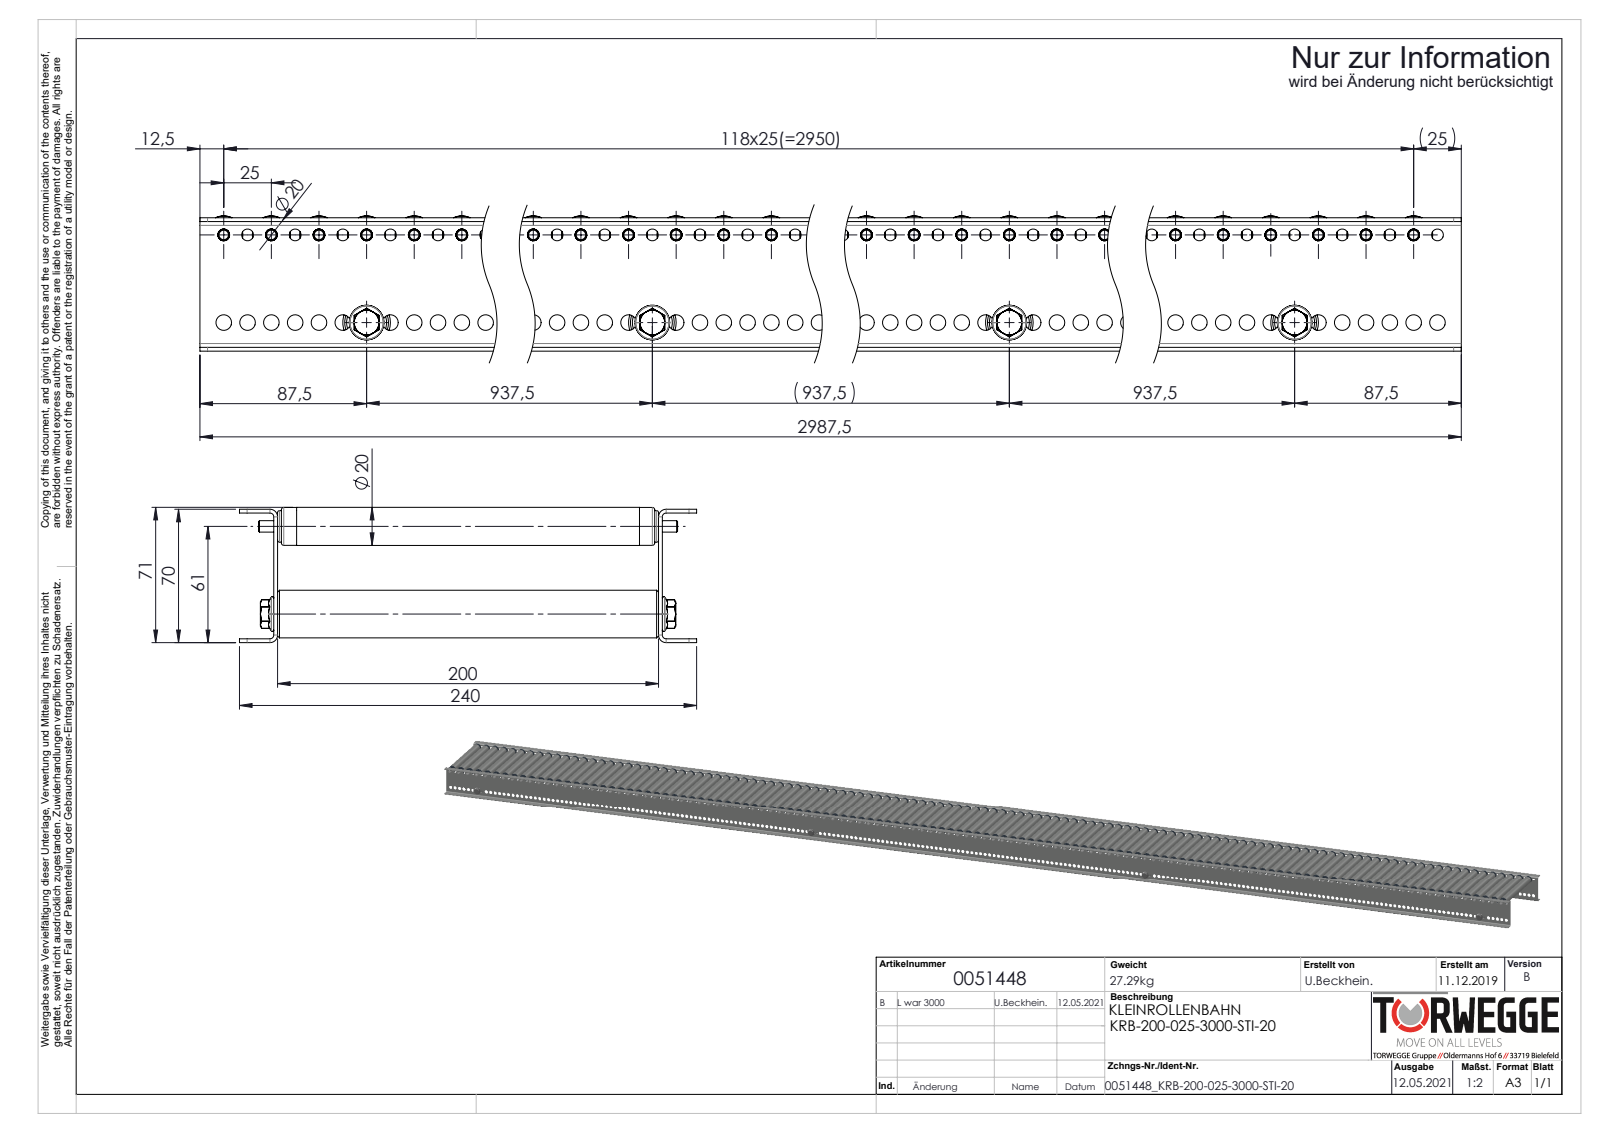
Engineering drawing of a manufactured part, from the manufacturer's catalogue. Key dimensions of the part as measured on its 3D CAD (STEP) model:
Part name (STEP PRODUCT): Profil_KRB-20x70x20x2_KFG_S109089_U-PROFIL-20-70-20-2-KRB-20-L=2987,5; 0039777_Achse-Ø06-FA-KFG_L=220 fr D20; S100993_Tragrollenrohr-Ø20x1STI_KFG_L=180; 0051448 (+4 more)
STEP written by: SolidWorks 2020 (AUTOMOTIVE_DESIGN)
Units: millimetres
Bodies: 260 solids, 23356 faces (7582 planar, 8902 cylindrical, 6872 other)
Overall size (bounding box): 2987.5 × 240 × 71
Volume: 3 347 000 mm³ · Surface area: 5 196 000 mm²
Round holes (diameter × count): ⌀6.2 ×238, ⌀8.2 ×238, ⌀6.1 ×119, ⌀14.2 ×119, ⌀17.2 ×119, ⌀18 ×119, ⌀6.8 ×4, ⌀21 ×4
Round bosses / shafts (diameter × count): ⌀20 ×119, ⌀19.9 ×119, ⌀18.1 ×119, ⌀17.8 ×119, ⌀16.5 ×119, ⌀6 ×119, ⌀25 ×4, ⌀8 ×4
Partial cylindrical surfaces — rounded edges, fillets, slot ends (radius × count): R4.05 ×119, R4 ×8, R2 ×4
Main face-to-face distances: 2, 202, 68, 200, 204, 70, 66, 192, 18, 30
Hole centre spacings: 12.5, 25, 37.5, 50, 62.5, 75, 87.5, 100
